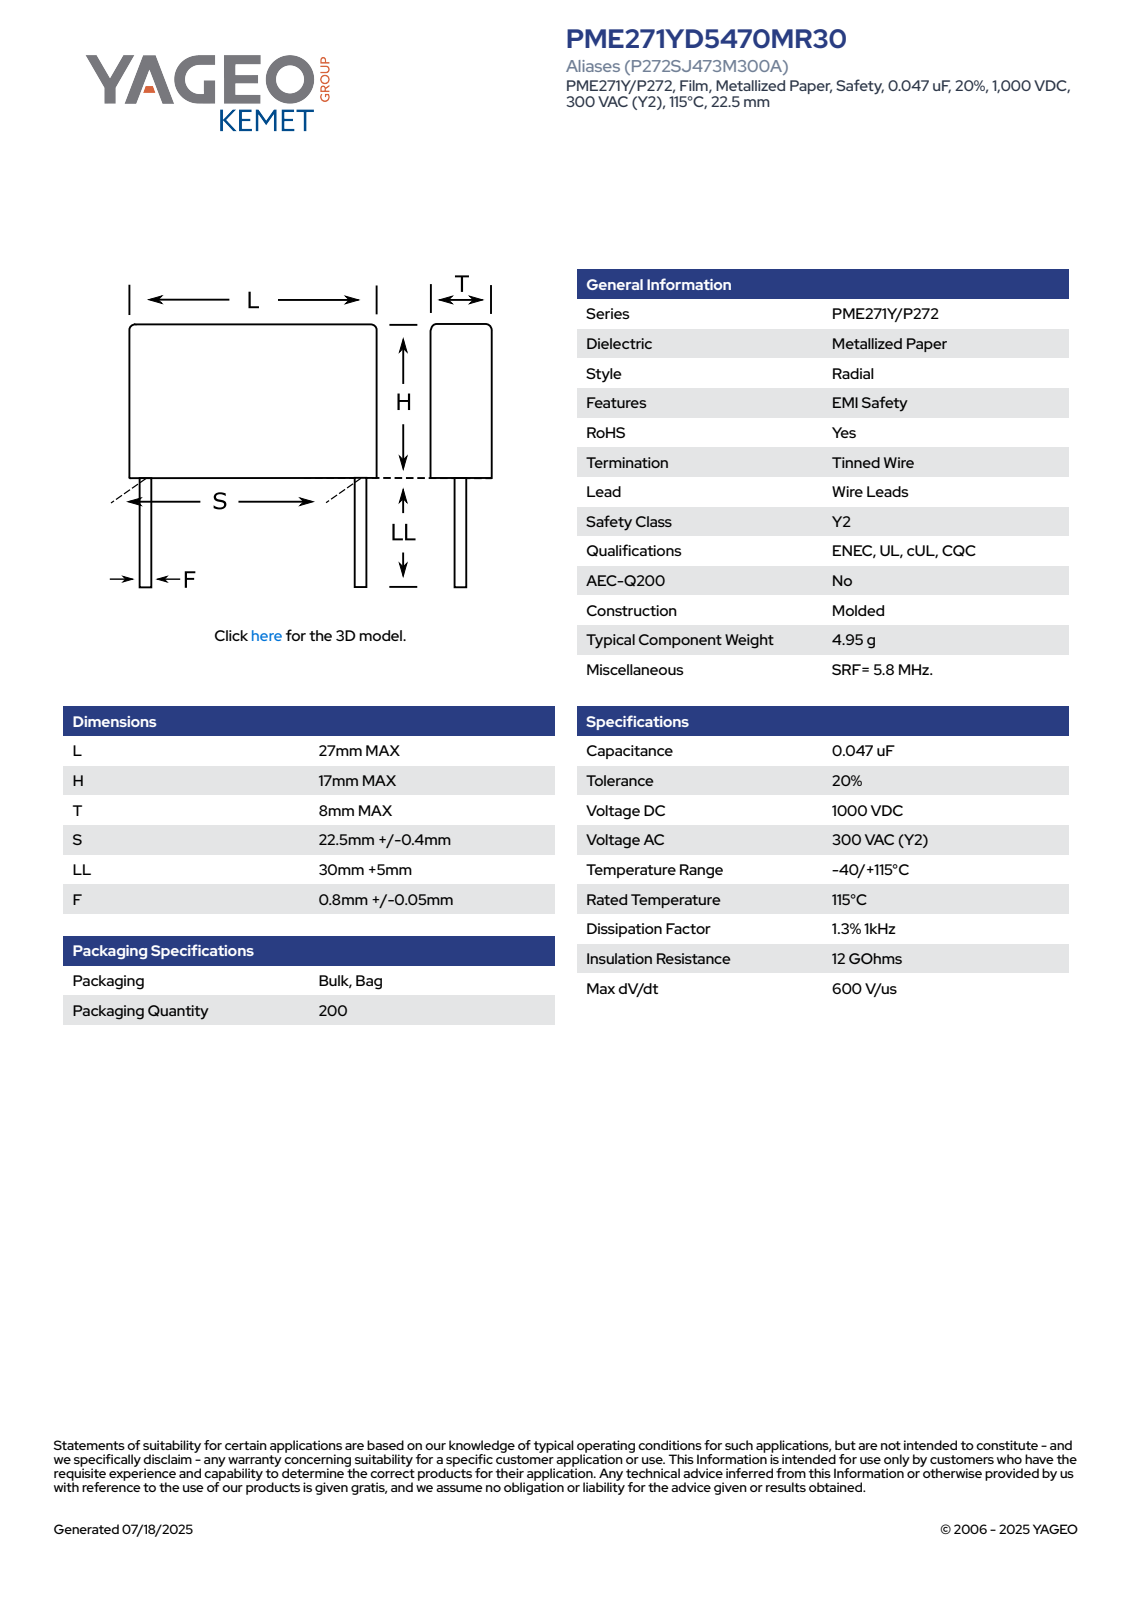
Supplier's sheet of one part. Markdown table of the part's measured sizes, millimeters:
| quantity | value |
| --- | --- |
| part name | CFR_MOLDED_27X17X8_L27H17T8S22.5LL35F0.85 |
| STEP written by | SolidWorks 2014 (AUTOMOTIVE_DESIGN) |
| units | millimeters |
| bodies | 4 solids, 73 faces (65 planar, 8 cylindrical, 0 other) |
| overall size | 52 × 27 × 8.01 |
| volume | 3 708 mm³ |
| surface area | 1 829 mm² |
| round bosses / shafts (diameter × count) | 0.85 × 2 |
| partial cylindrical surfaces (radius × count) | 0.5 × 4 |
| main face-to-face distances | 8, 17, 27, 8.01, 35, 52, 44.55, 9.55, 7.45, 42.13 |
